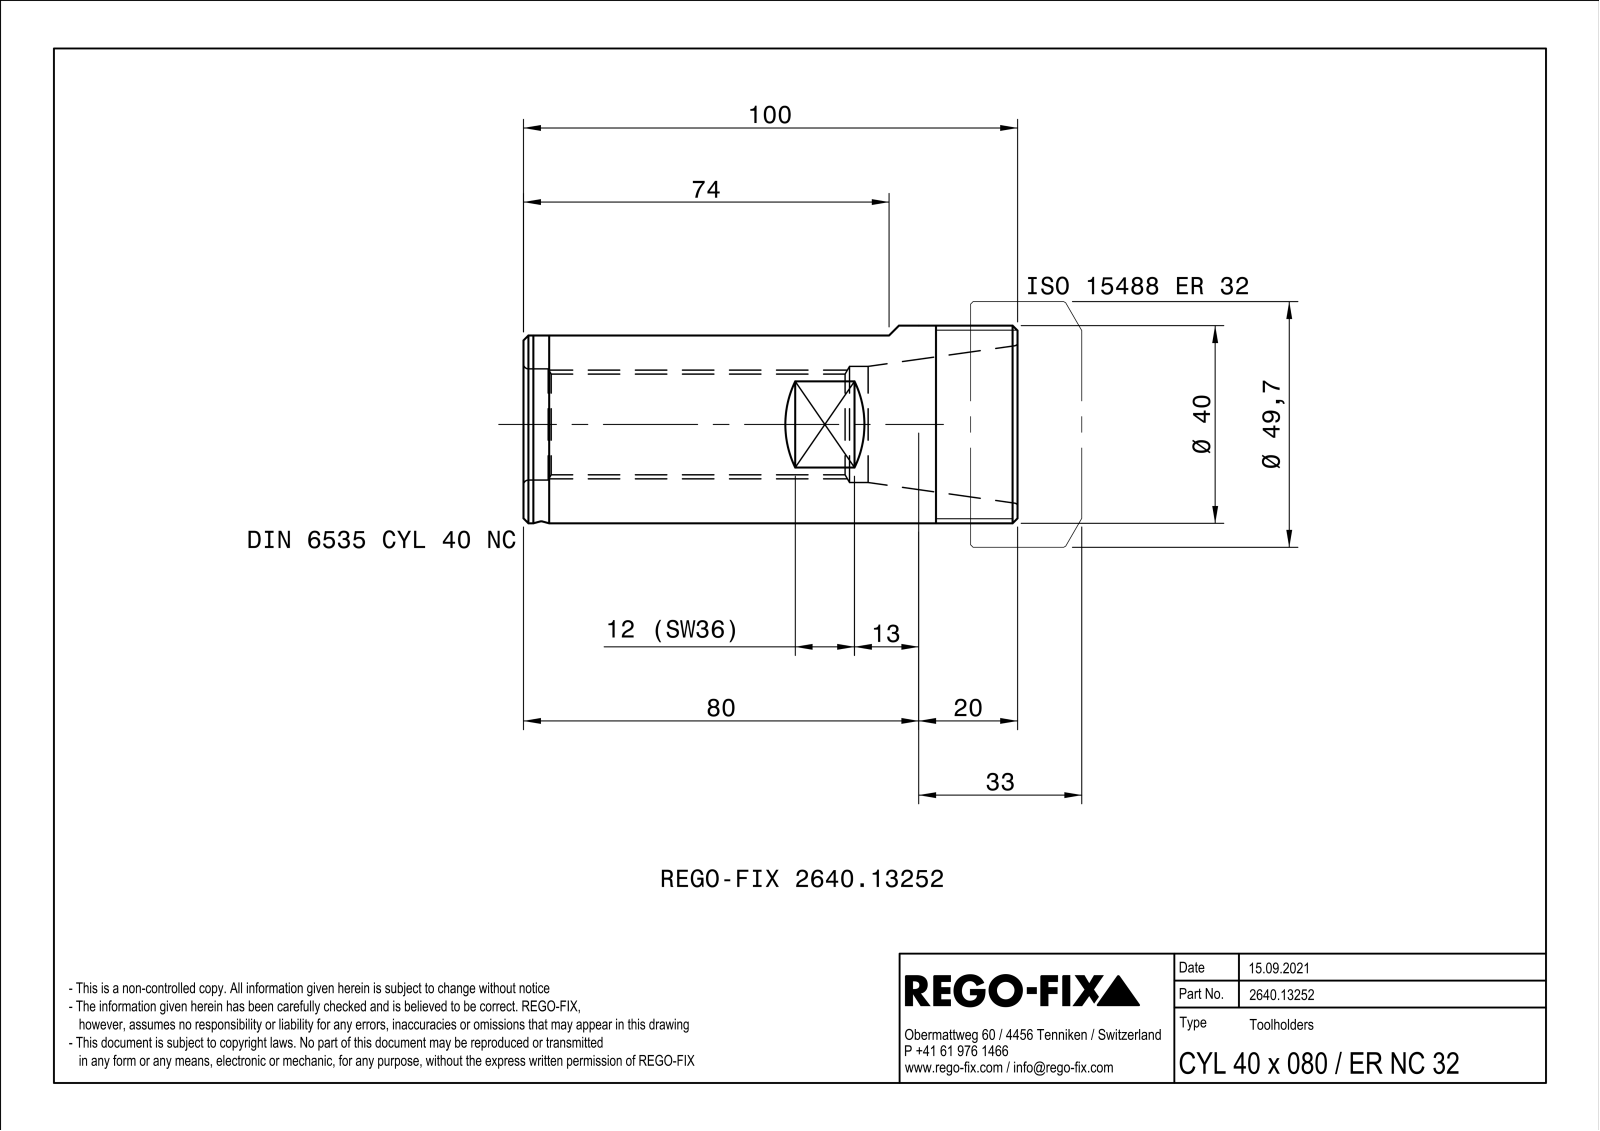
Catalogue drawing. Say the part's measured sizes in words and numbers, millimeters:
The part is named "NOCUT". Its 3-D file was written by "SIEMENS PLM Software Solid Edge ST10 (AUTOMOTIVE_DESIGN)". It is 1 solid with 27 faces: 11 planar, 6 cylindrical and 10 other. Overall it measures 100 by 40 by 40 millimeters. Its volume is 81 039 cubic millimeters and its surface area 20 959 square millimeters. Round holes: 1 of diameter 20.38, 1 of diameter 22.5, 1 of diameter 23.5. Round bosses or shafts: 1 of diameter 40. The main face-to-face distances are 100, 36, 16.97, 51.61.
